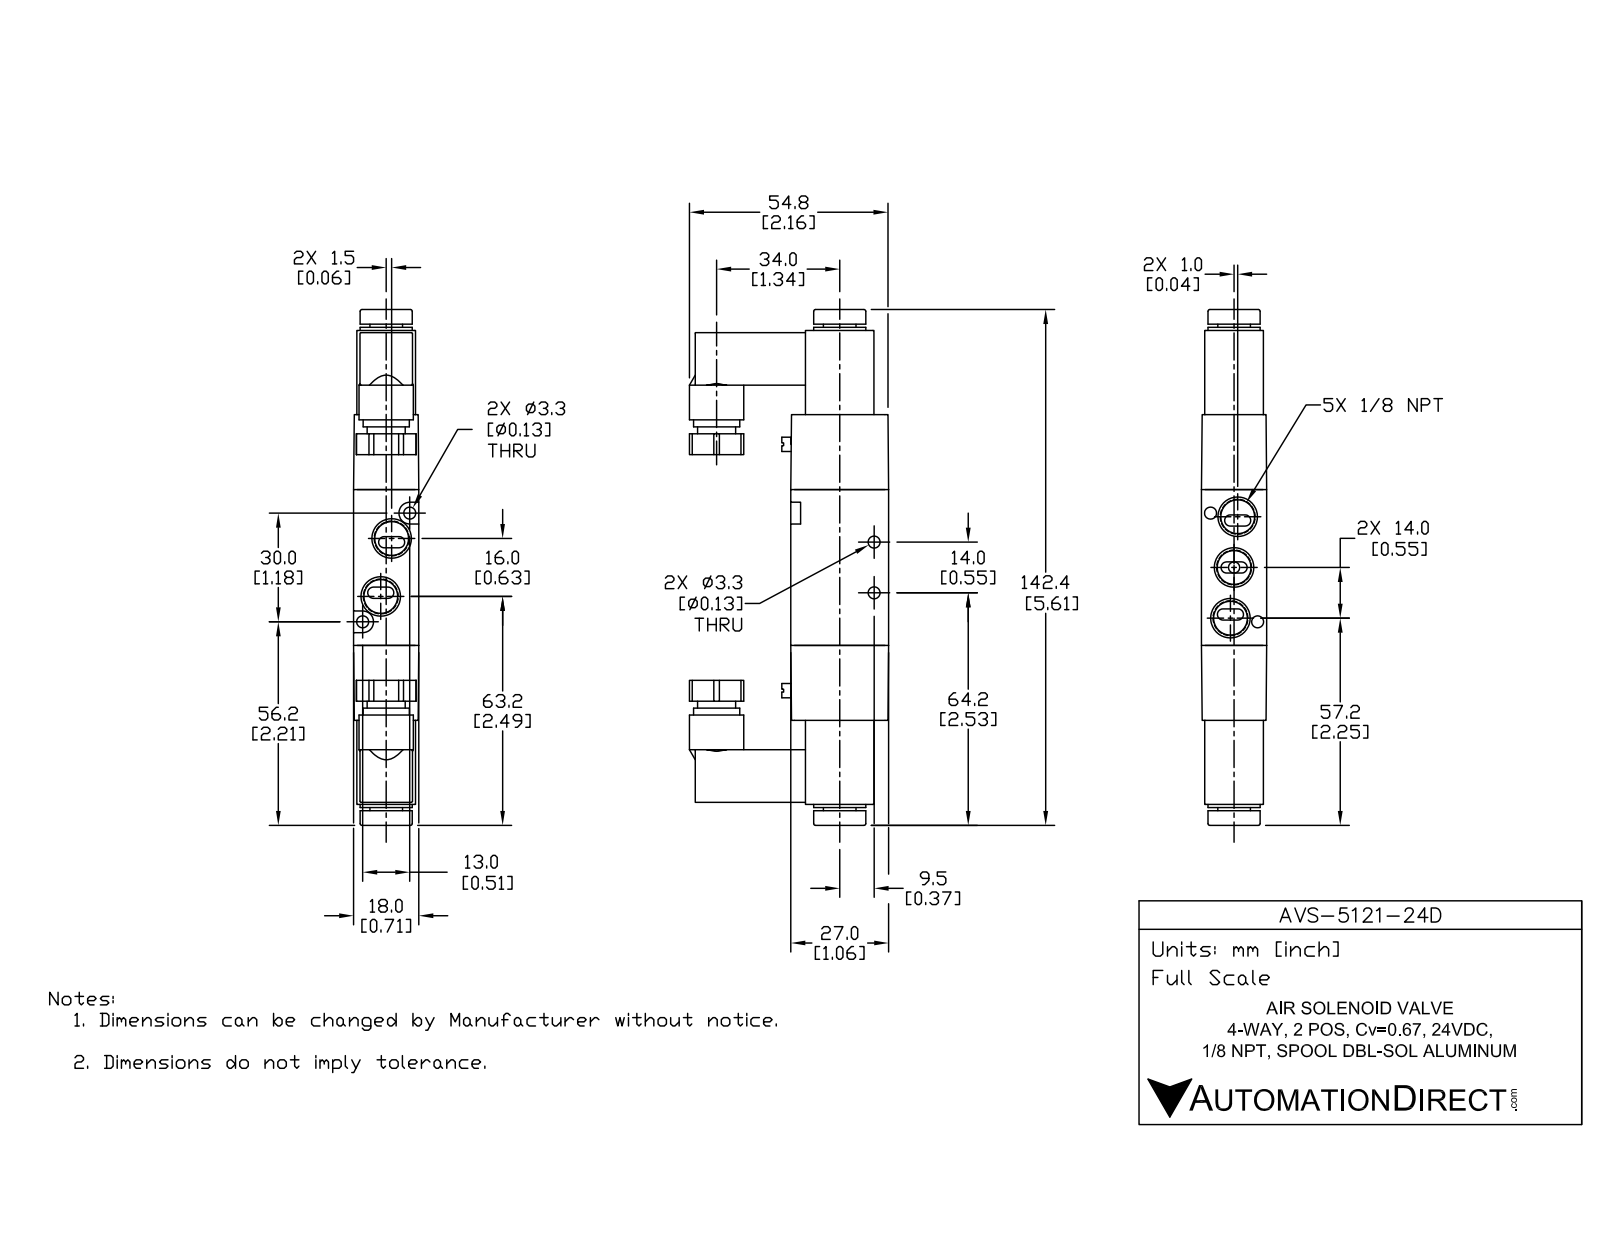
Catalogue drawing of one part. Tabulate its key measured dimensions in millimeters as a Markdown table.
| quantity | value |
| --- | --- |
| part name | AVS-5121-24D |
| STEP written by | SolidWorks 2015 (CONFIG_CONTROL_DESIGN) |
| units | millimeters |
| bodies | 5 solids, 254 faces (131 planar, 91 cylindrical, 32 other) |
| overall size | 142.6 × 55 × 18 |
| volume | 69 237 mm³ |
| surface area | 23 595 mm² |
| round holes (diameter × count) | 8.43 × 5, 3.3 × 3, 3.2 × 1, 9.3 × 1 |
| round bosses / shafts (diameter × count) | 6.8 × 2, 15 × 1, 14.4 × 1, 12.8 × 1, 10.5 × 1, 9 × 1 |
| partial cylindrical surfaces (radius × count) | 1.54 × 10, 0.3 × 8, 0.5 × 8, 1 × 8, 3 × 2 |
| main face-to-face distances | 1.75, 16.25, 0.81, 17.57, 14.5, 18, 18.38, 43, 23.52, 3.86 |
| hole center spacings | 7.57, 14.04, 16.35, 29.52, 6.25, 6.82, 8.04, 8.19 |
